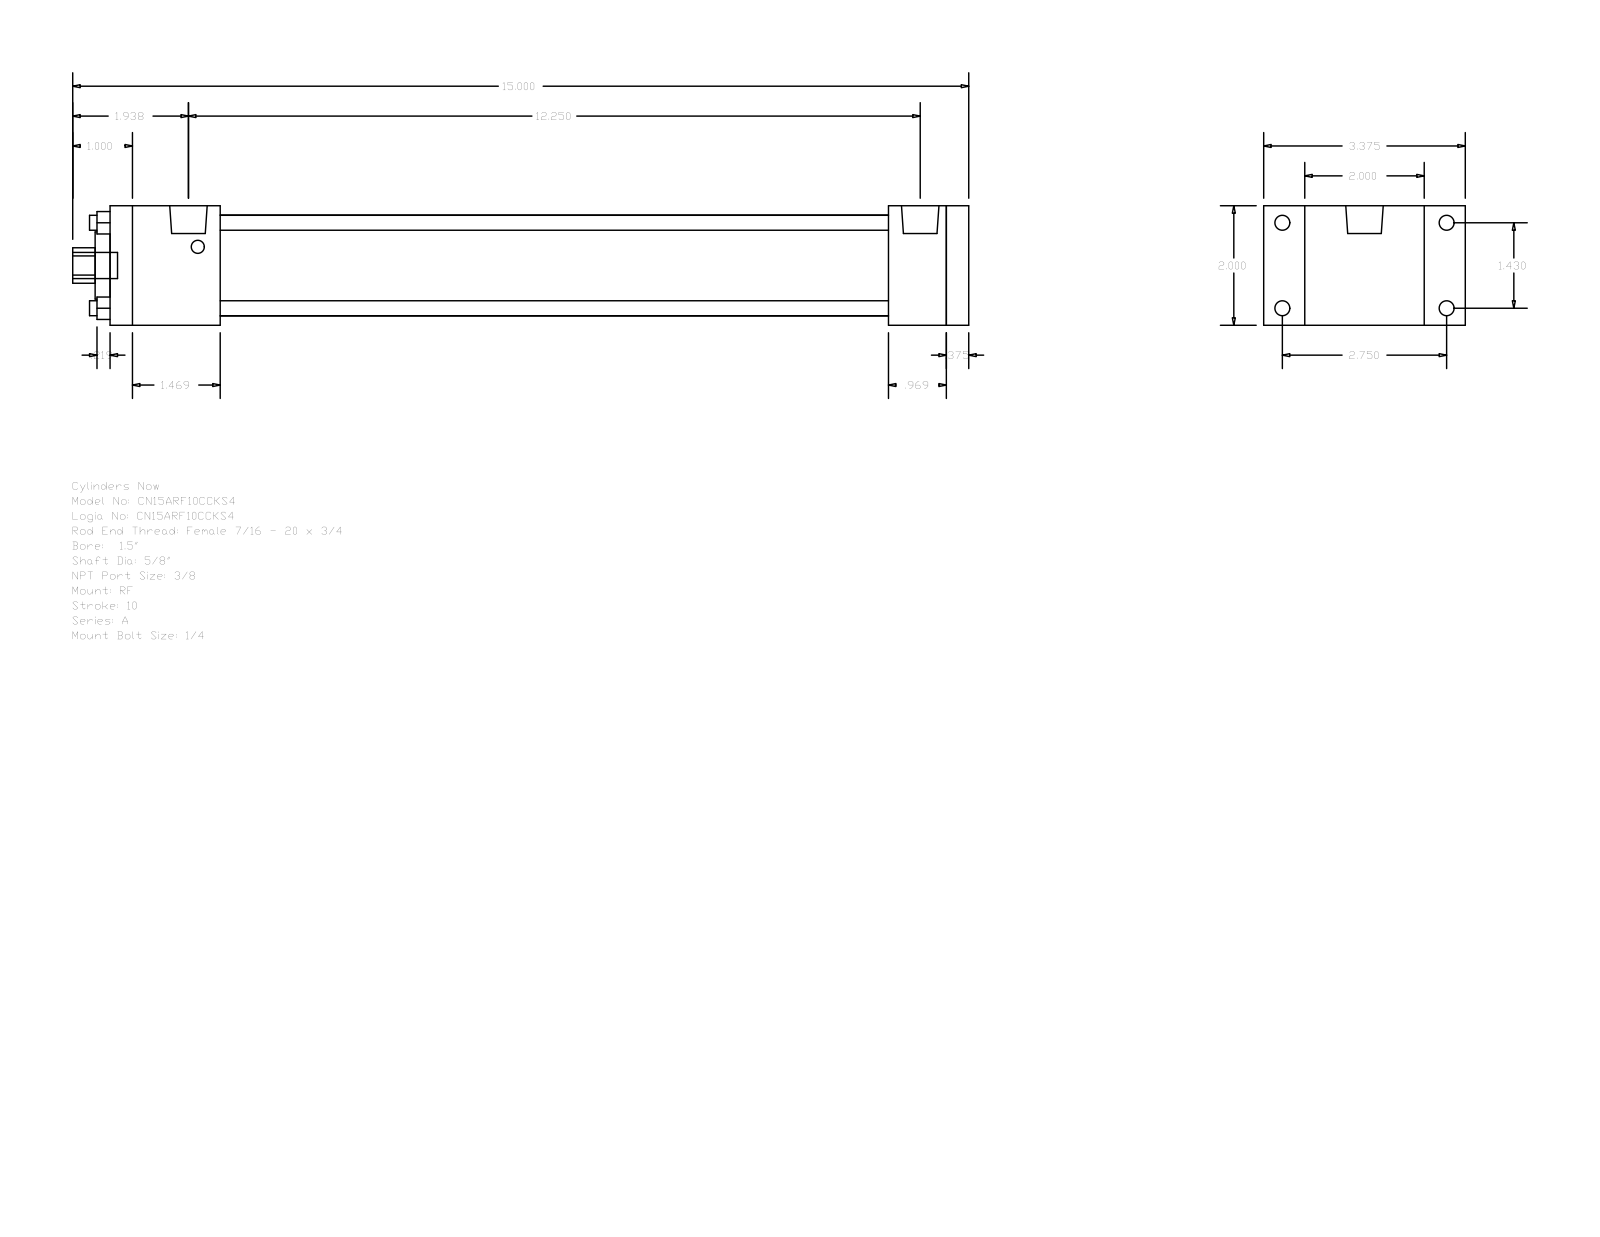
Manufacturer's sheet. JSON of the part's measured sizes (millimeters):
{"part_name": "A_RF__0150_0.625", "step_written_by": "GSSL Pune (CONFIG_CONTROL_DESIGN)", "units": "millimeters", "bodies": {"solids": 0, "faces": 92, "planar": 64, "cylindrical": 28, "other": 0}, "overall_size": [381, 85.72, 50.8], "round_holes": [[6.35, 4], [15.88, 1], [28.57, 1], [42.93, 1]], "round_bosses_or_shafts": [[6.35, 4], [5.56, 4], [15.93, 2], [11.11, 1]], "partial_cylinders_radius": [[7.54, 1]], "face_to_face_distances": [50.8, 9.52, 355.6, 365.12, 330.99, 24.61, 34.13, 46.83, 284.16, 308.77], "hole_center_spacings": [25.68, 36.32, 51.36]}
